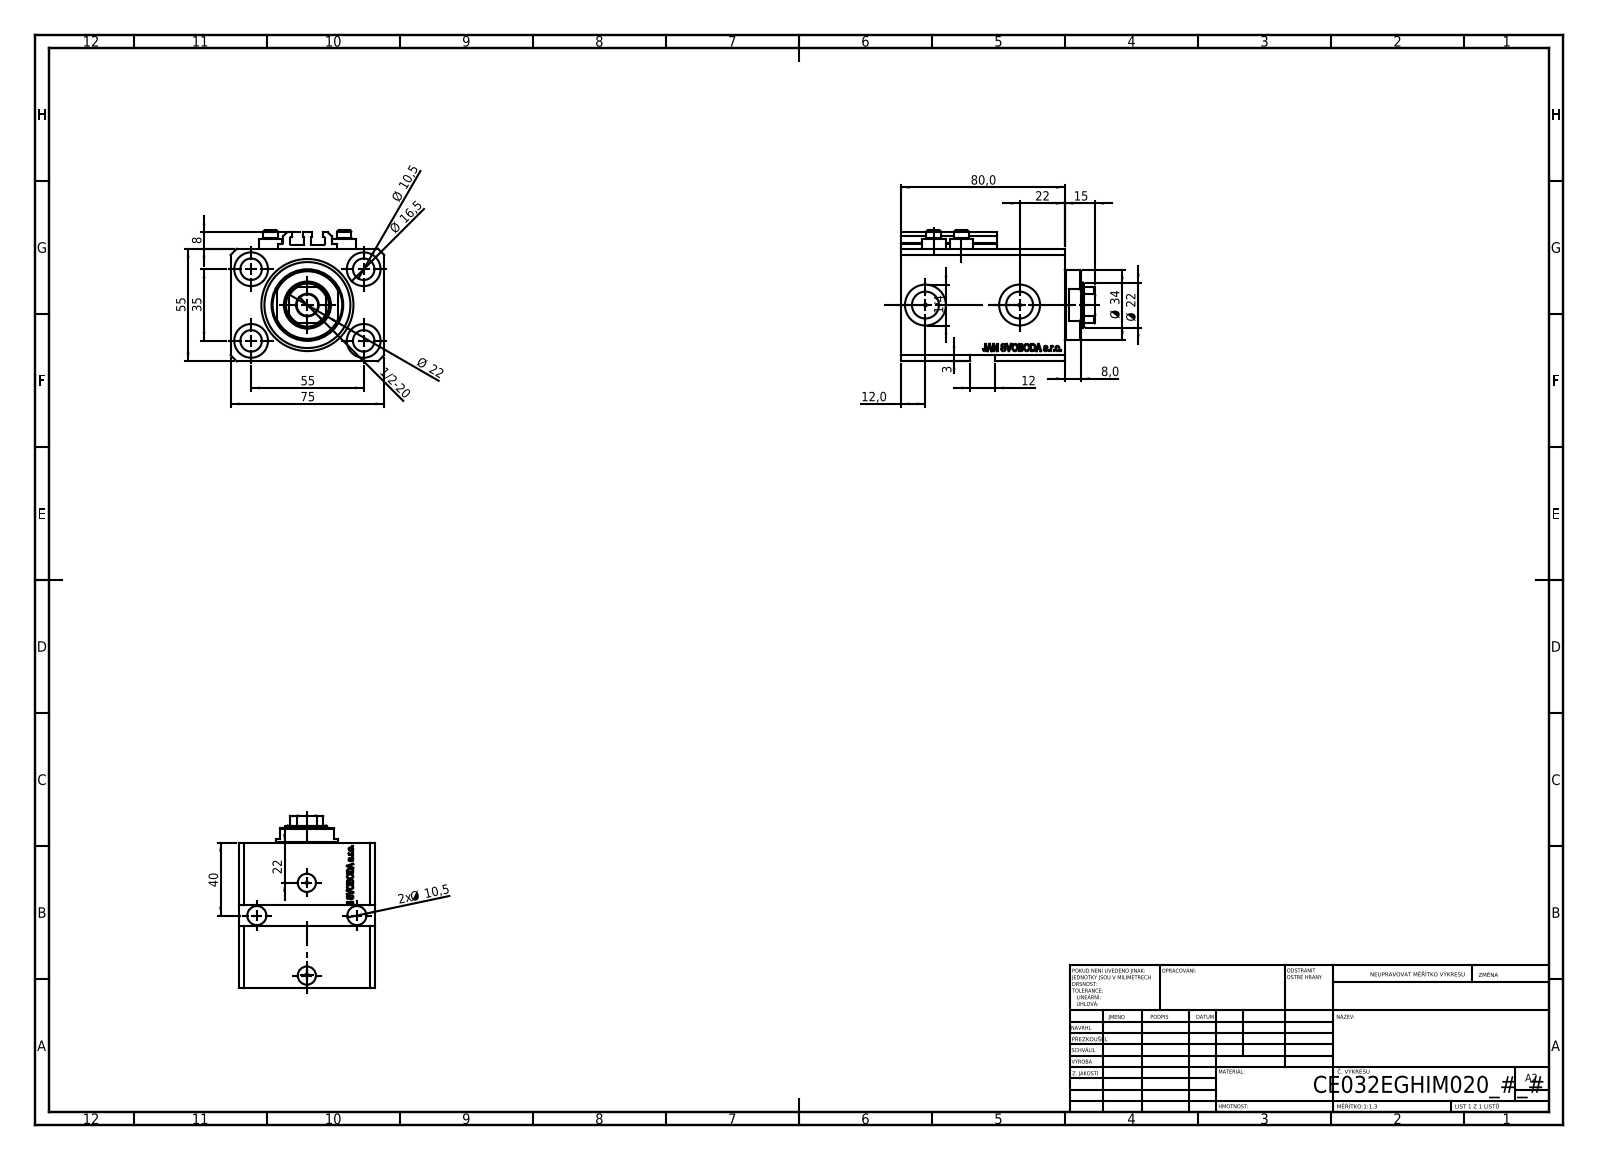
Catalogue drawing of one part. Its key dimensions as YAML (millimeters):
part_name: "V250CE_E_Body; V250CE_C_VCP; ALLEN BOLT V250CE; V250CE_VC_E"
step_written_by: "SolidWorks 2019 (CONFIG_CONTROL_DESIGN)"
units: millimeters
bodies: {solids: 8, faces: 1064, planar: 514, cylindrical: 126, other: 424}
overall_size: [95, 75, 64]
volume: 283894
surface_area: 74463
round_holes:
  - {diameter: 10.5, count: 7}
  - {diameter: 1.25, count: 4}
  - {diameter: 4, count: 4}
  - {diameter: 16.5, count: 4}
  - {diameter: 10, count: 2}
  - {diameter: 13.16, count: 2}
  - {diameter: 20, count: 2}
  - {diameter: 22, count: 1}
  - {diameter: 32, count: 1}
  - {diameter: 45, count: 1}
round_bosses_or_shafts:
  - {diameter: 11.6, count: 4}
  - {diameter: 7, count: 4}
  - {diameter: 34, count: 1}
partial_cylinders:
  - {radius: 0.2, count: 10}
  - {radius: 10.5, count: 1}
face_to_face_distances: [55, 75, 15, 80, 65, 3, 55.1, 9.9, 70.1, 54]
hole_center_spacings: [32.6, 55, 13.6, 14.09, 19.89, 20.12, 25.81, 28.48]
